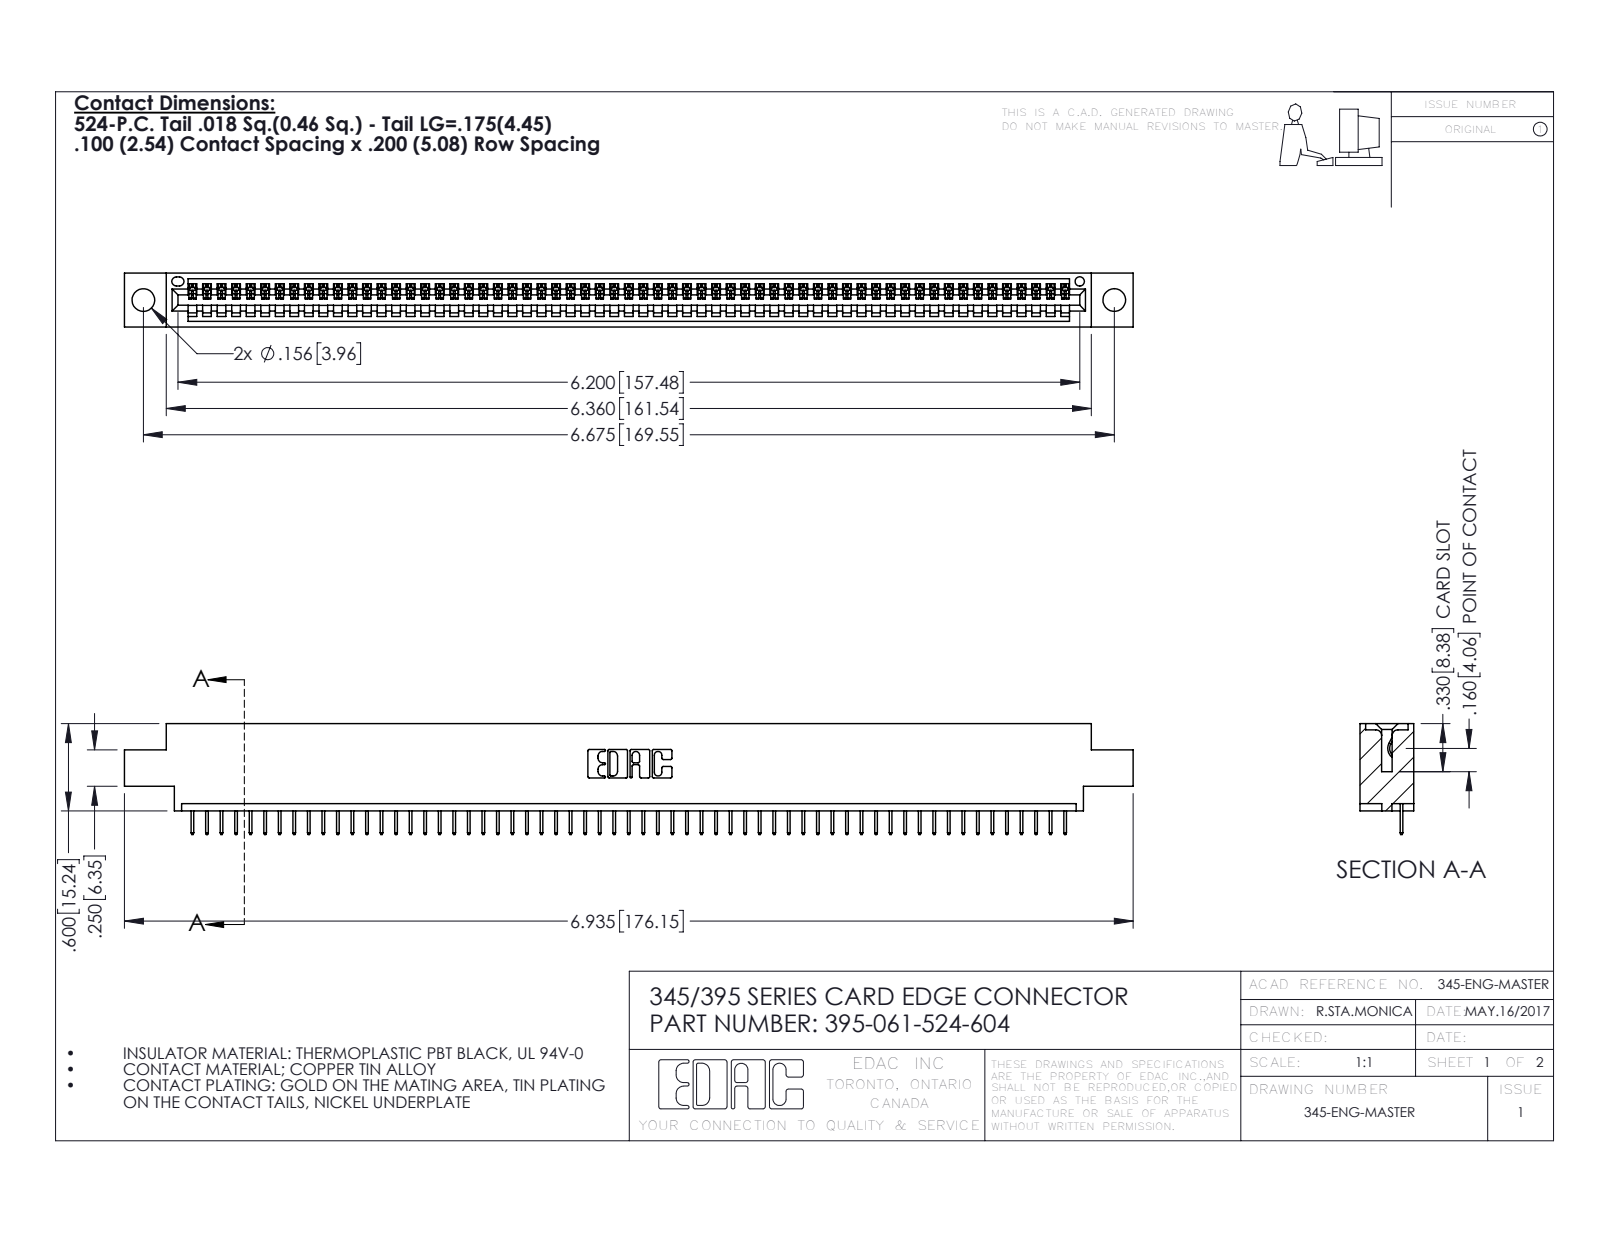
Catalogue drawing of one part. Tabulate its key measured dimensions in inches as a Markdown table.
| quantity | value |
| --- | --- |
| part name | 395-061-524-604; 345 Part_0.170 Offset - 0.156 Dia-TH; 345-292-001_345-293-124 |
| STEP written by | SolidWorks 2016 (CONFIG_CONTROL_DESIGN) |
| units | inches |
| bodies | 62 solids, 3912 faces (2890 planar, 1022 cylindrical, 0 other) |
| overall size | 6.935 × 0.762 × 0.37 |
| volume | 1.003 in³ |
| surface area | 32.98 in² |
| round holes (diameter × count) | 0.156 × 2, 0.064 × 1 |
| partial cylindrical surfaces (radius × count) | 0.006 × 122, 0.01 × 22, 0.007 × 6, 0.031 × 6, 0.026 × 3, 0.031 × 2, 0.04 × 2, 0.014 × 1 |
| main face-to-face distances | 0.072, 0.298, 0.37, 0.2, 0.098, 0.272, 0.025, 0.225, 0.072, 0.175 |
| hole center spacings | 0.27, 6.439, 6.675 |
